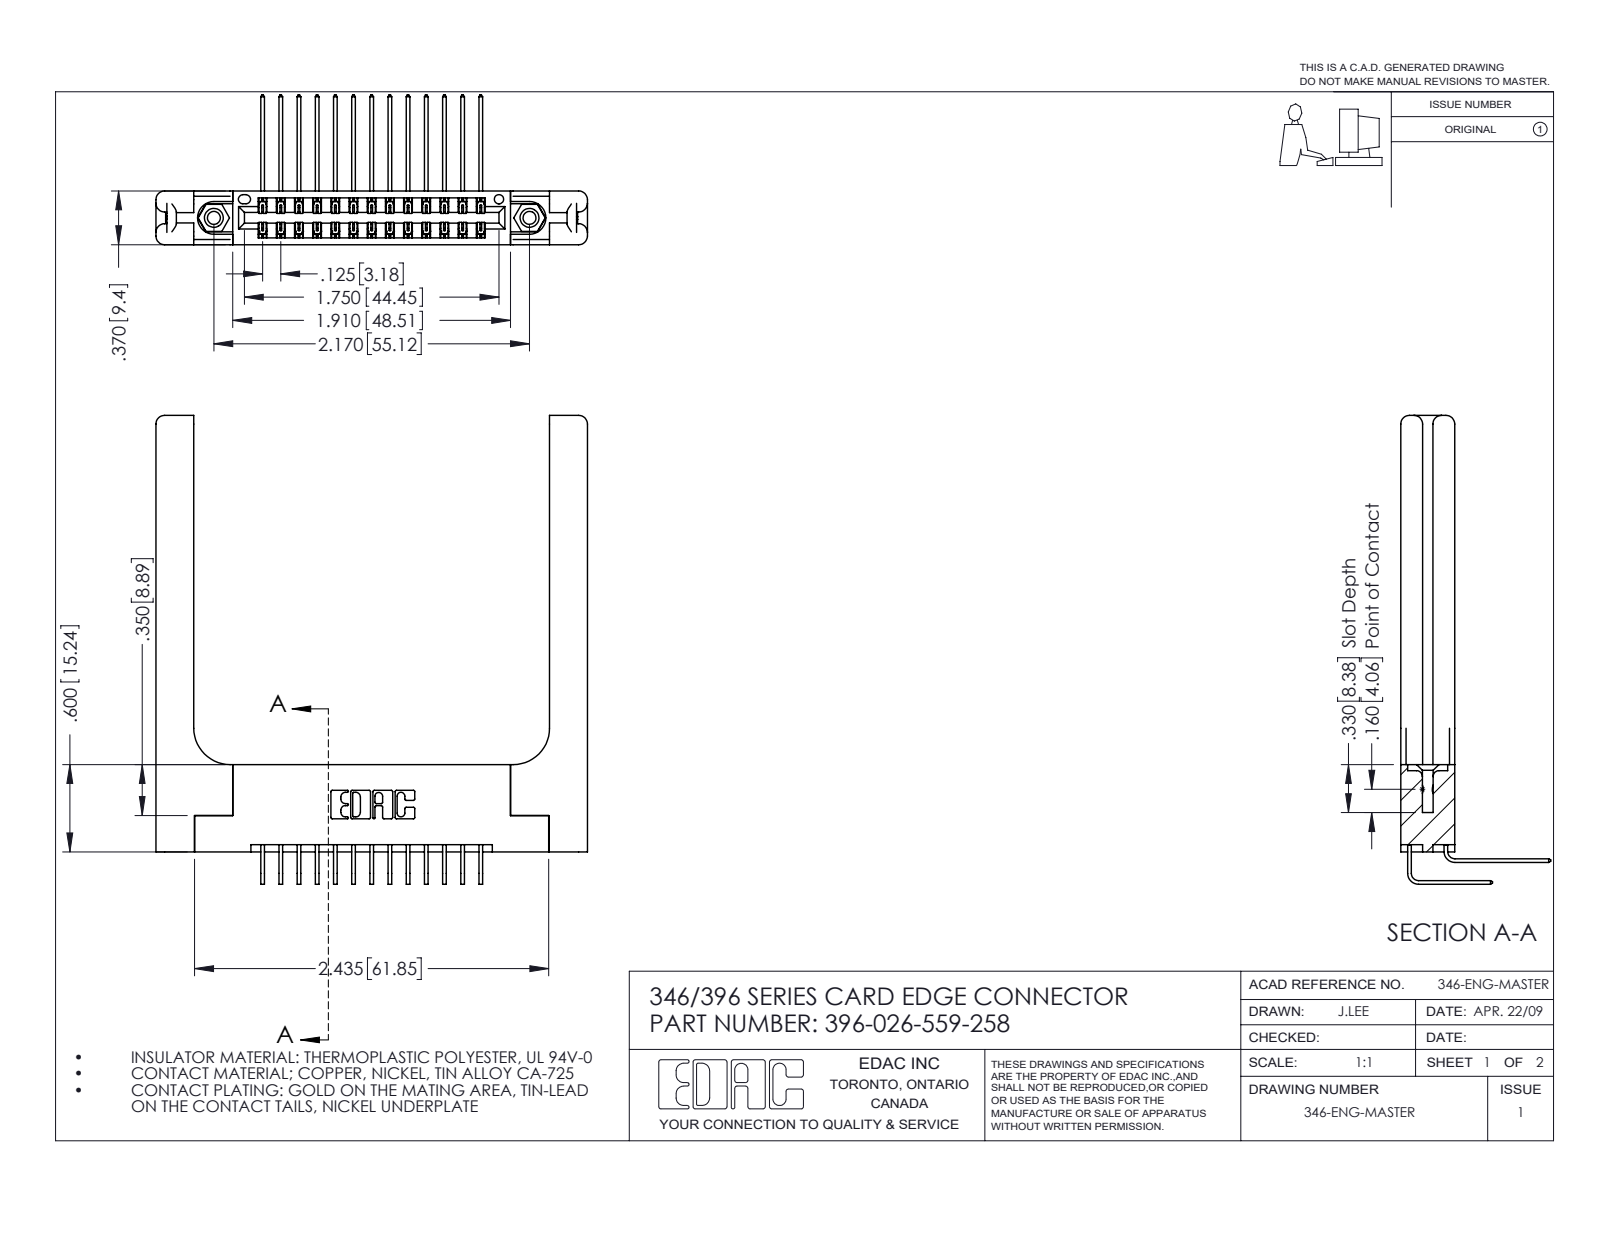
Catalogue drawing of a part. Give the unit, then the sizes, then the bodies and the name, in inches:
Units: inches
Overall size (bounding box): 3.223 × 2.966 × 1.03
Round holes (diameter × count): ⌀0.089 ×2, ⌀0.125 ×2, ⌀0.156 ×2, ⌀0.064 ×1
Round bosses / shafts (diameter × count): ⌀0.155 ×2
Partial cylindrical surfaces — rounded edges, fillets, slot ends (radius × count): R0.006 ×39, R0.01 ×22, R0.06 ×16, R0.007 ×6, R0.031 ×6, R0.026 ×3, R0.014 ×2, R0.022 ×2
Main face-to-face distances: 0.37, 0.15, 0.072, 0.048, 0.322, 0.148, 0.025, 0.25, 0.102, 0.22
Hole centre spacings: 0.246, 1.964, 2.17
Volume: 0.901 in³ · Surface area: 23.61 in²
Bodies: 31 solids, 1782 faces (1186 planar, 536 cylindrical, 60 other)
Part name (STEP PRODUCT): 346-220-058_345-220-058; 396-026-559-258; 345-292-001_559 Tail - 2; 346 Part_Flush Mounting Lugs - 0.156 Dia-TH (+2 more)
STEP written by: SolidWorks 2016 (CONFIG_CONTROL_DESIGN)
